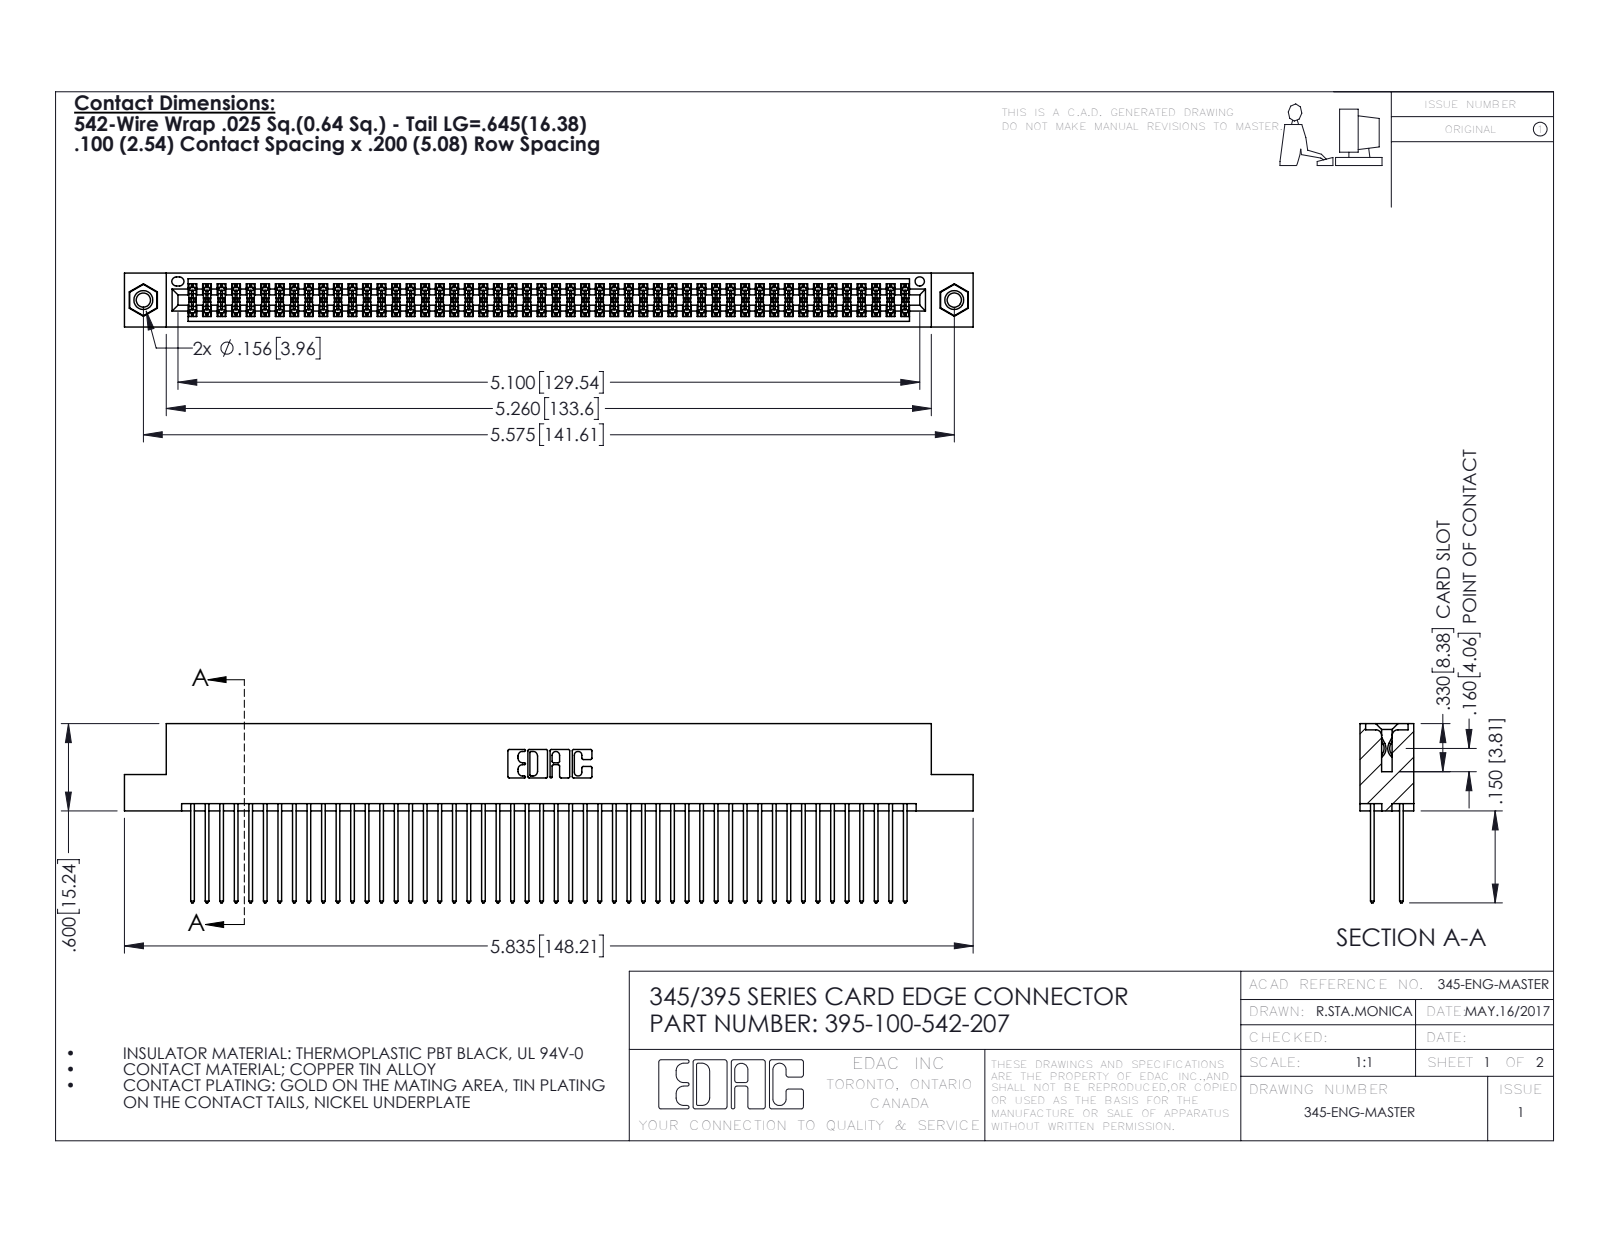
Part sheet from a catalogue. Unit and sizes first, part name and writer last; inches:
Units: inches
Overall size (bounding box): 5.835 × 1.232 × 0.37
Round holes (diameter × count): ⌀0.098 ×2, ⌀0.125 ×2, ⌀0.156 ×2, ⌀0.064 ×1
Round bosses / shafts (diameter × count): ⌀0.155 ×2
Partial cylindrical surfaces — rounded edges, fillets, slot ends (radius × count): R0.006 ×150, R0.01 ×100, R0.01 ×22, R0.007 ×6, R0.031 ×6, R0.026 ×3, R0.014 ×2, R0.019 ×2
Main face-to-face distances: 0.072, 0.298, 0.2, 0.098, 0.272, 0.025, 0.225, 0.37, 0.175, 0.149
Hole centre spacings: 0.27, 5.339, 5.575
Volume: 0.911 in³ · Surface area: 37.85 in²
Bodies: 103 solids, 5186 faces (3412 planar, 1758 cylindrical, 16 other)
Part name (STEP PRODUCT): 345-292-001_345-293-142; 345 Part_Flush Mounting Lugs - 0.156 Dia-TI; 345-250-001_345-250-005-103; 395-100-542-207
STEP written by: SolidWorks 2016 (CONFIG_CONTROL_DESIGN)
